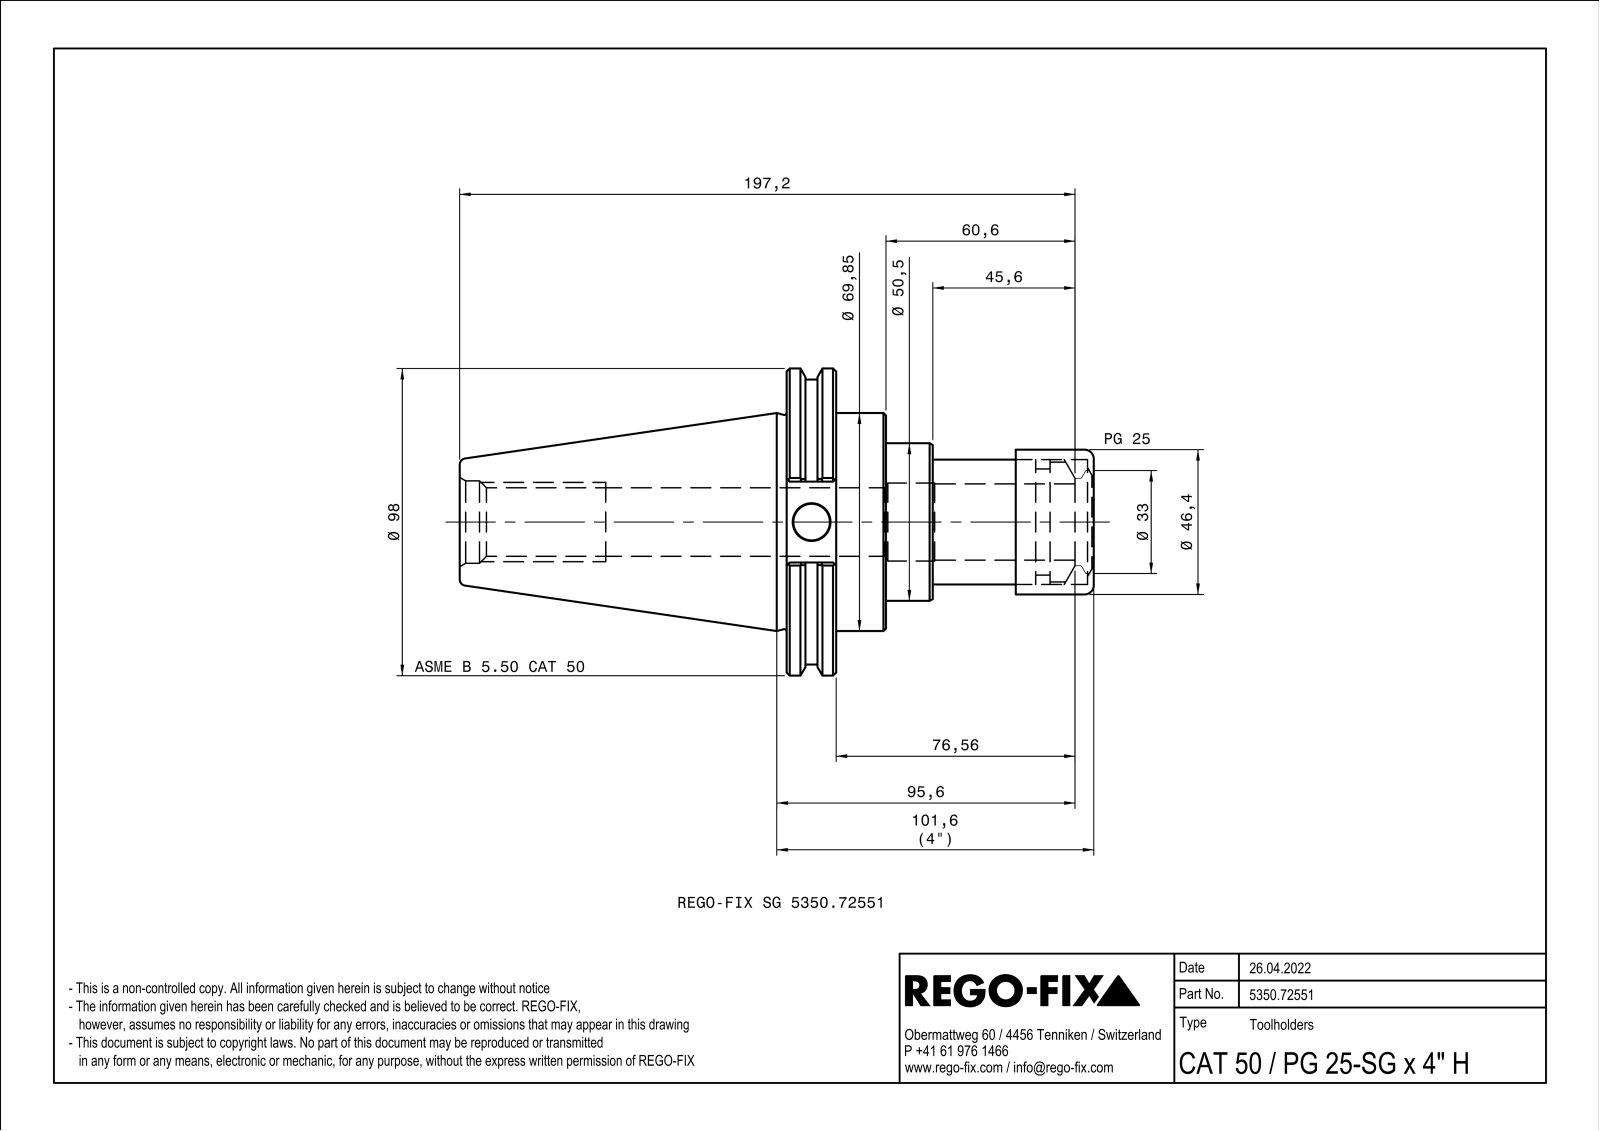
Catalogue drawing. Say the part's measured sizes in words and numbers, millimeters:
The part is named "NOCUT". Its 3-D file was written by "SIEMENS PLM Software Solid Edge ST10 (AUTOMOTIVE_DESIGN)". It is 1 solid with 120 faces: 38 planar, 31 cylindrical and 51 other. Overall it measures 203.2 by 98.42 by 94.39 millimeters. Its volume is 437 823 cubic millimeters and its surface area 68 214 square millimeters. Round holes: 1 of diameter 11.7, 1 of diameter 21.96, 1 of diameter 25, 1 of diameter 26.4, 1 of diameter 30, 1 of diameter 40.05, 1 of diameter 42. Round bosses or shafts: 1 of diameter 98.42, 1 of diameter 91.3, 1 of diameter 69.85, 1 of diameter 50.5, 1 of diameter 46.4, 1 of diameter 46, 1 of diameter 40, 1 of diameter 34. Partial cylindrical surfaces (rounded edges, fillets, slot ends): 12 of radius 0.5. The main face-to-face distances are 15.87, 15.96, 31.83, 66.6, 82.56, 98.43, 203.2, 136.6, 120.64, 104.77.
